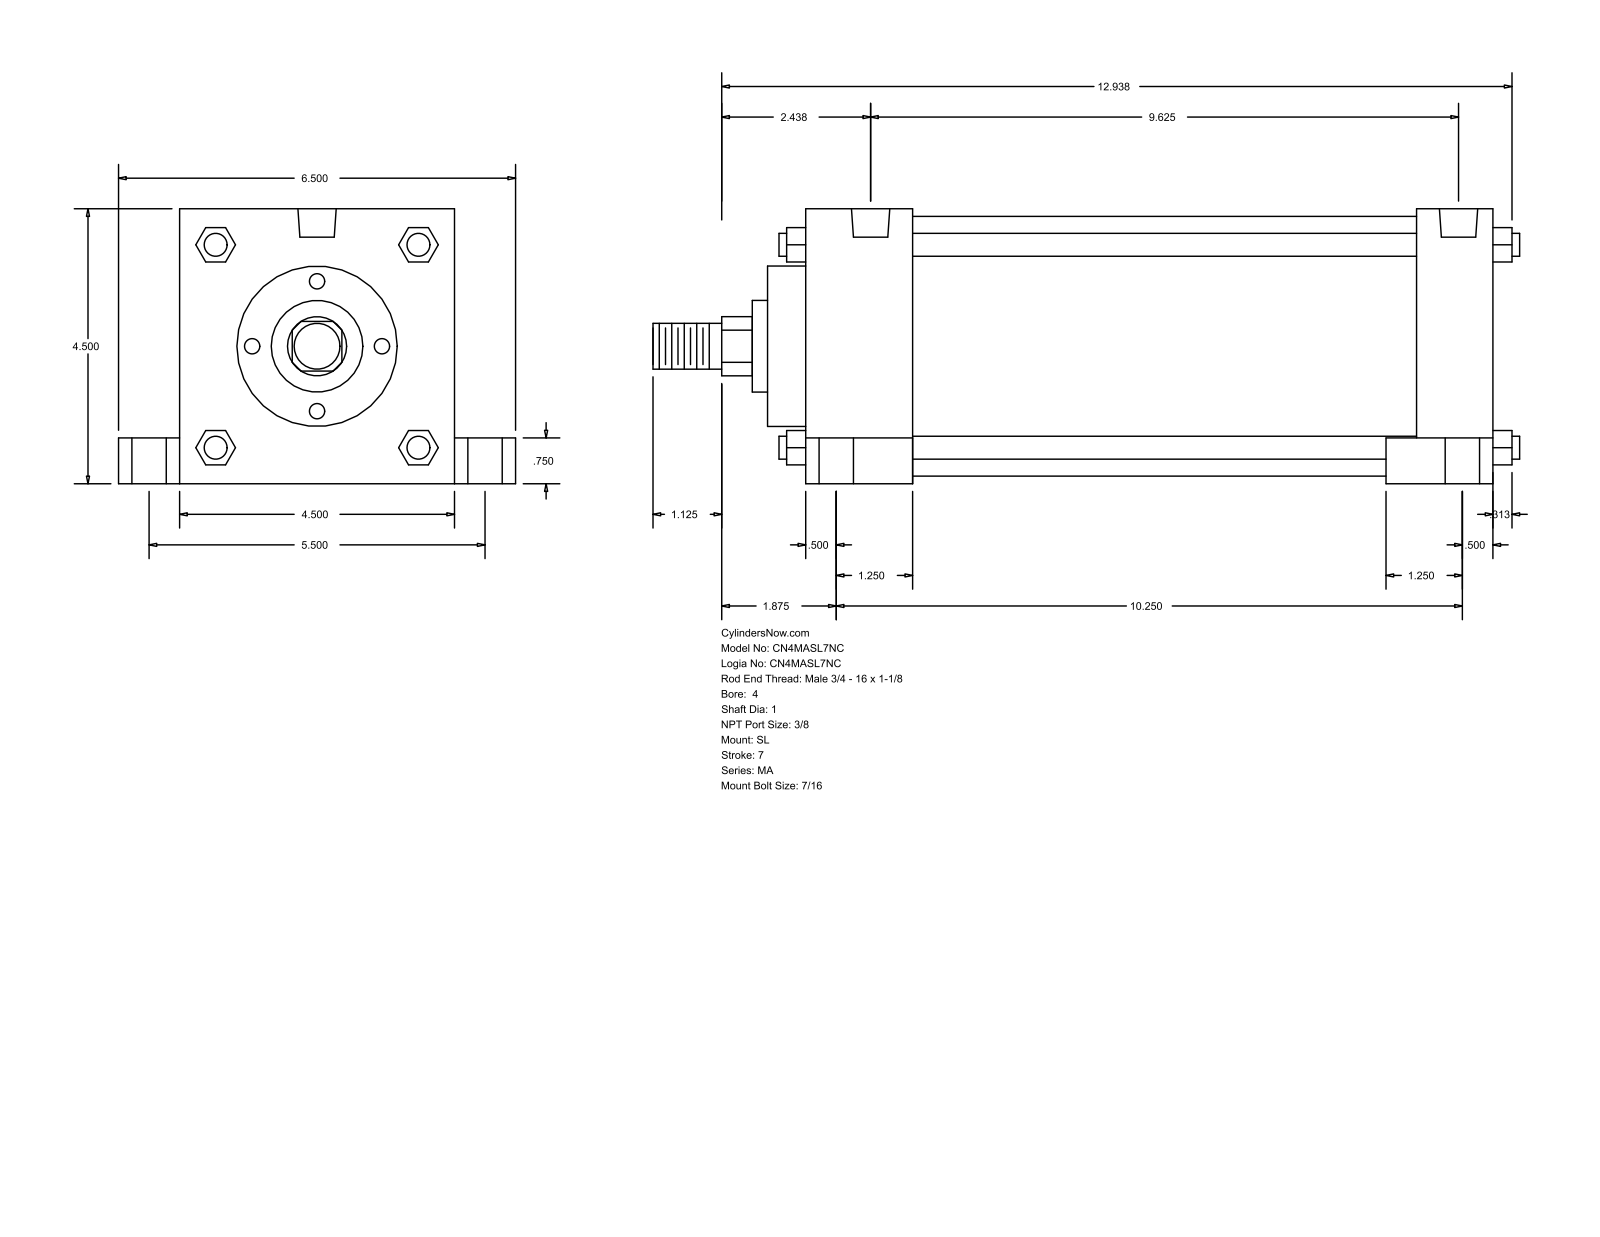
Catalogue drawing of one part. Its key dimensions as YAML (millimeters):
part_name: "MA_SL__0400_1"
step_written_by: "GSSL Pune (CONFIG_CONTROL_DESIGN)"
units: millimeters
bodies: {solids: 0, faces: 150, planar: 113, cylindrical: 37, other: 0}
overall_size: [360.36, 165.1, 114.3]
round_holes:
  - {diameter: 11.11, count: 4}
  - {diameter: 14.29, count: 4}
  - {diameter: 20.64, count: 4}
  - {diameter: 15.93, count: 2}
round_bosses_or_shafts:
  - {diameter: 9.53, count: 4}
  - {diameter: 107.95, count: 1}
  - {diameter: 66.67, count: 1}
  - {diameter: 38.1, count: 1}
  - {diameter: 25.4, count: 1}
  - {diameter: 19.05, count: 1}
partial_cylinders:
  - {radius: 12.29, count: 1}
face_to_face_distances: [114.3, 285.76, 209.55, 44.46, 241.3, 254.01, 31.75, 25.4, 139.7, 19.05]
hole_center_spacings: [69.87, 70.14, 71.3, 72.4, 139.7, 234.95, 251.22, 255.79]
